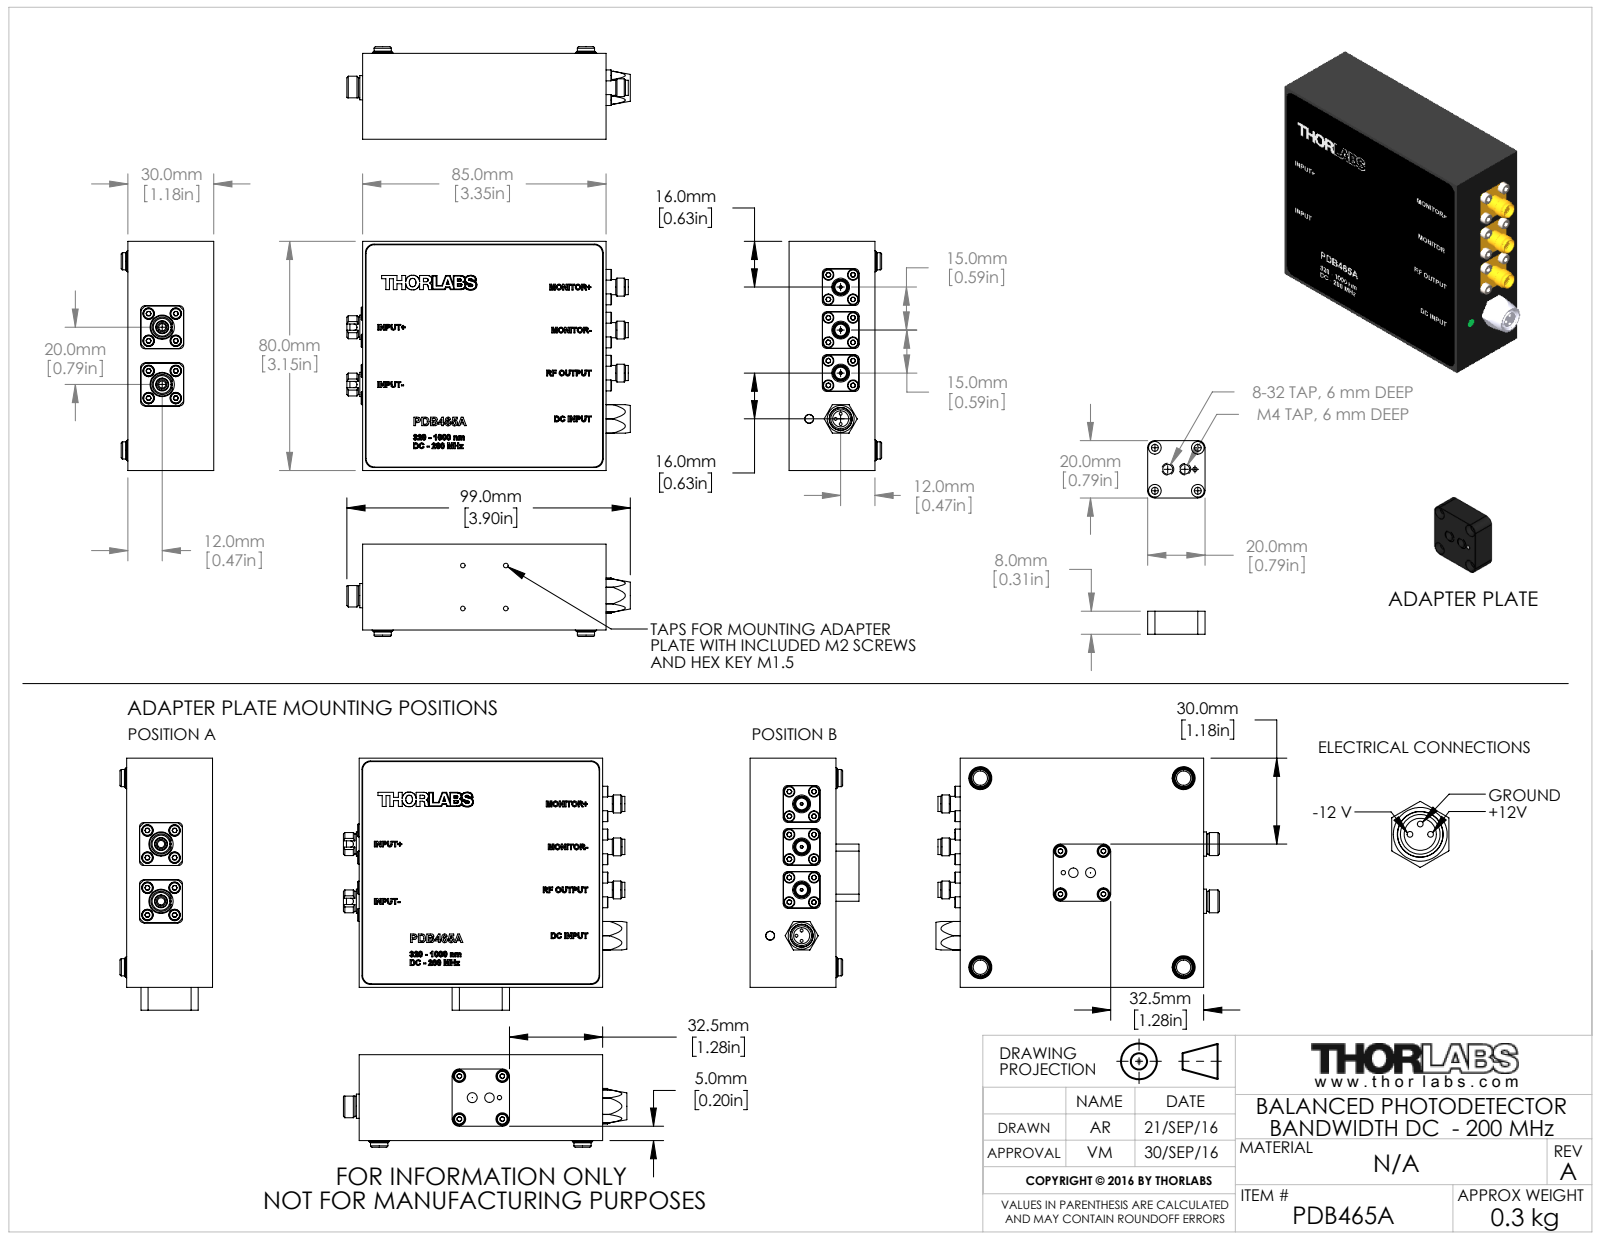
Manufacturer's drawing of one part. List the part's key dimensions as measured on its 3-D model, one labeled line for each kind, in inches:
Part name (STEP PRODUCT): MTN005461-E0W
STEP written by: SolidWorks 2014 (AUTOMOTIVE_DESIGN)
Units: inches
Bodies: 90 solids, 3040 faces (1750 planar, 584 cylindrical, 706 other)
Overall size (bounding box): 3.898 × 3.465 × 1.496
Volume: 5.353 in³ · Surface area: 89.6 in²
Round holes (diameter × count): ⌀0.063 ×38, ⌀0.102 ×12, ⌀0.087 ×8, ⌀0.094 ×8, ⌀0.157 ×8, ⌀0.173 ×8, ⌀0.04 ×6, ⌀0.315 ×5, ⌀0.031 ×3, ⌀0.039 ×3, ⌀0.161 ×3, ⌀0.165 ×3
Round bosses / shafts (diameter × count): ⌀0.15 ×20, ⌀0.079 ×20, ⌀0.177 ×8, ⌀0.098 ×8, ⌀0.017 ×6, ⌀0.236 ×4, ⌀0.245 ×3, ⌀0.209 ×3
Partial cylindrical surfaces — rounded edges, fillets, slot ends (radius × count): R0.059 ×20, R0.118 ×12, R0.098 ×8, R0.197 ×8, R0.039 ×4, R0.374 ×2, R0.226 ×1
Main face-to-face distances: 1.169, 0.236, 0.933, 0.217, 3.15, 0.079, 2.933, 3.346, 0.138, 3.268
Hole centre spacings: 0.591, 0.239, 0.339, 0.374, 0.265, 0.344, 0.454, 0.508
